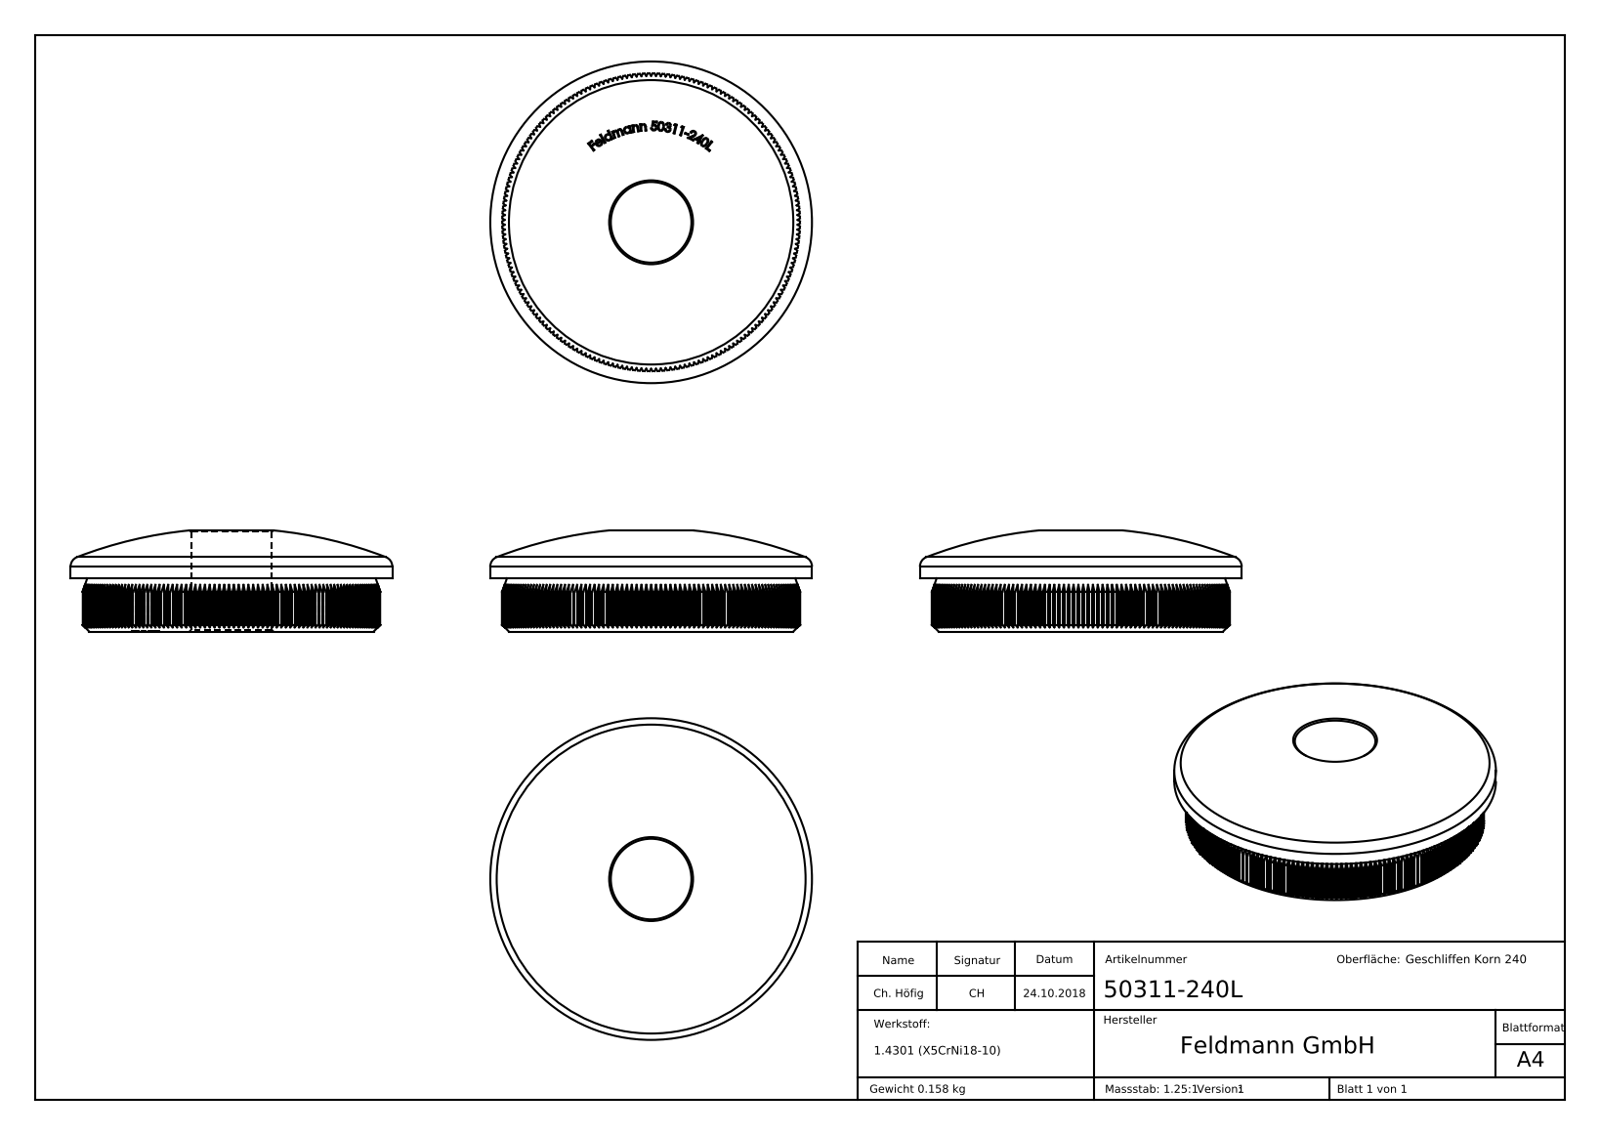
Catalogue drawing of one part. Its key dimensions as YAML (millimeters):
part_name: "50311-240L"
step_written_by: "SolidWorks 2015 (CONFIG_CONTROL_DESIGN)"
units: millimeters
bodies: {solids: 1, faces: 843, planar: 529, cylindrical: 194, other: 120}
overall_size: [48.3, 48.3, 15.19]
volume: 20008
surface_area: 6044
round_holes:
  - {diameter: 12.1, count: 1}
round_bosses_or_shafts:
  - {diameter: 48.3, count: 1}
partial_cylinders:
  - {radius: 22.35, count: 1}
face_to_face_distances: [8, 22, 21.98, 22.02, 7.9, 0.54, 10.97, 11.05, 11.09, 10.93]
